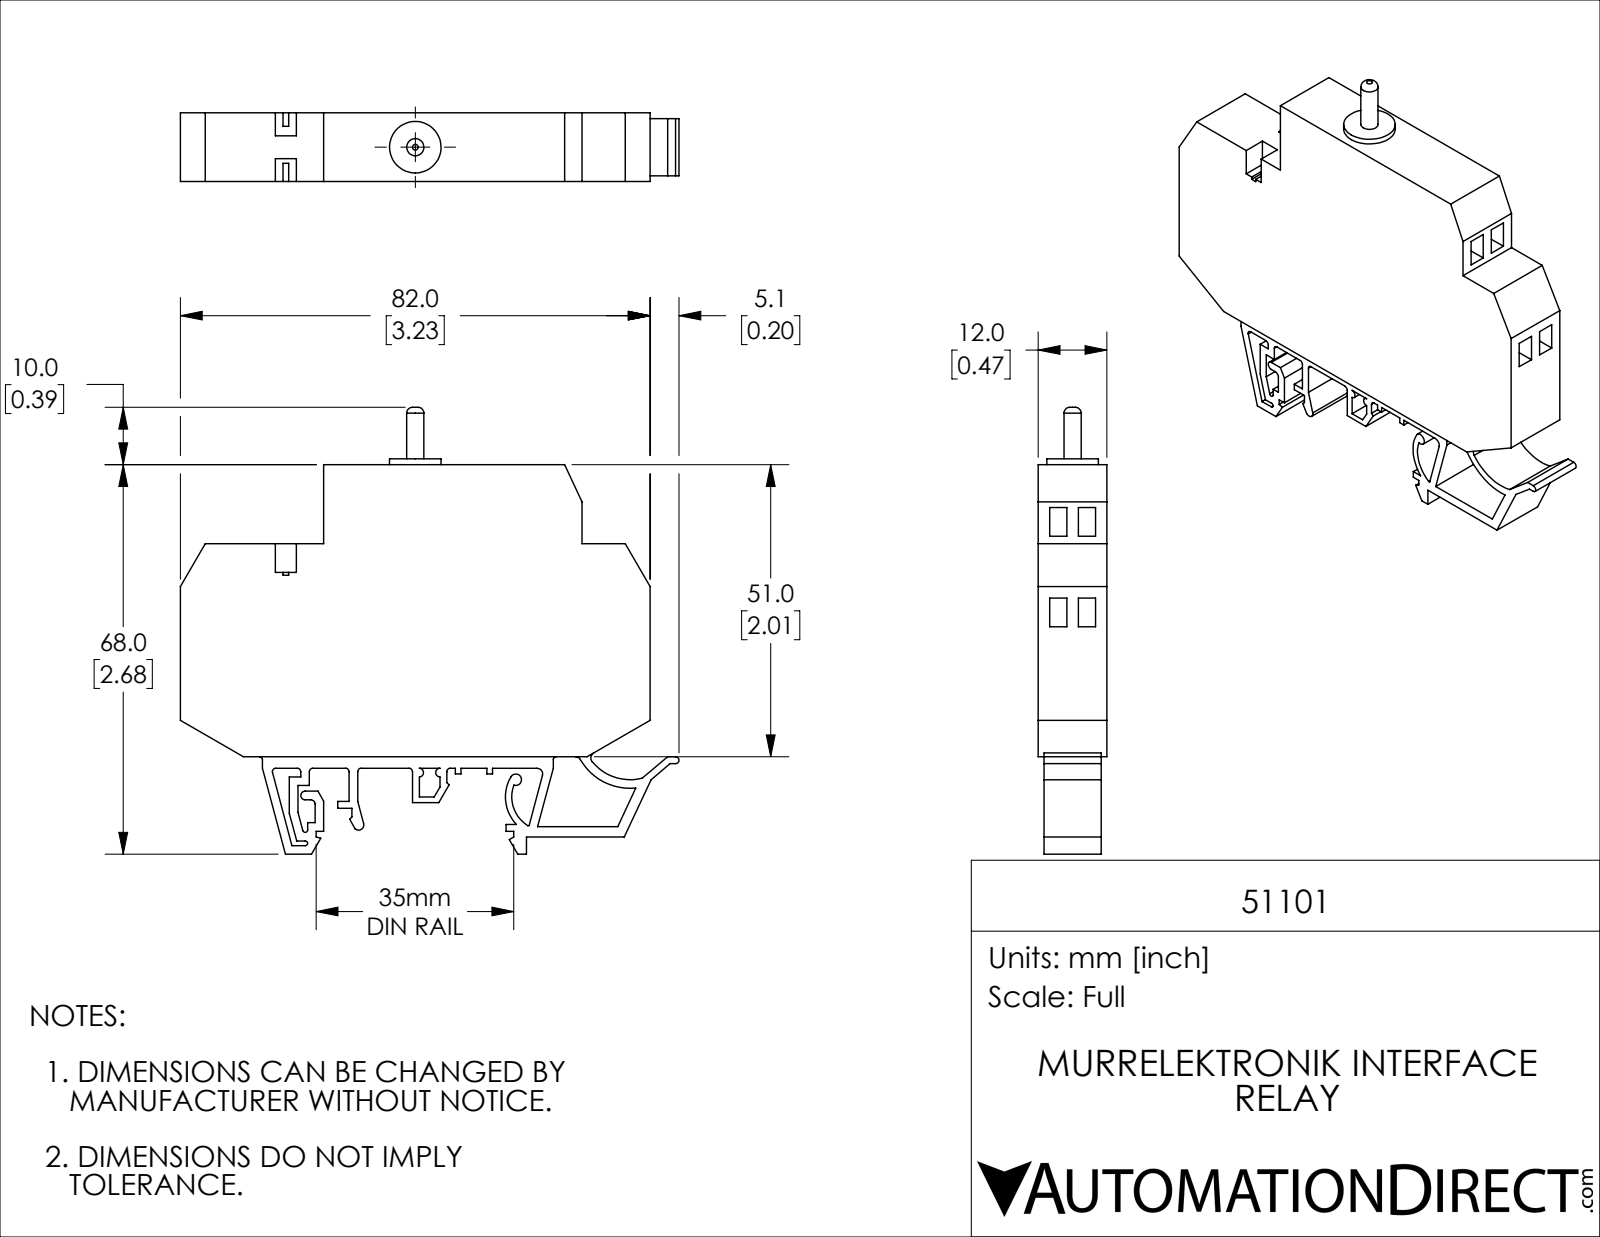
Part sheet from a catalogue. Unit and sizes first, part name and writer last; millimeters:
Units: millimetres
Overall size (bounding box): 87.1 × 78 × 12
Round bosses / shafts (diameter × count): ⌀9 ×1, ⌀3 ×1
Partial cylindrical surfaces — rounded edges, fillets, slot ends (radius × count): R0.6 ×8, R0.8 ×4, R1 ×4, R0.5 ×2, R0.4 ×1, R0.4 ×1, R0.9 ×1, R5.9 ×1
Main face-to-face distances: 12, 1, 11, 5, 2, 10, 1.5, 6, 53, 3
Volume: 45 540 mm³ · Surface area: 14 350 mm²
Bodies: 1 solid, 184 faces (147 planar, 35 cylindrical, 2 other)
Part name (STEP PRODUCT): 51101
STEP written by: SolidWorks 2019 (CONFIG_CONTROL_DESIGN)
